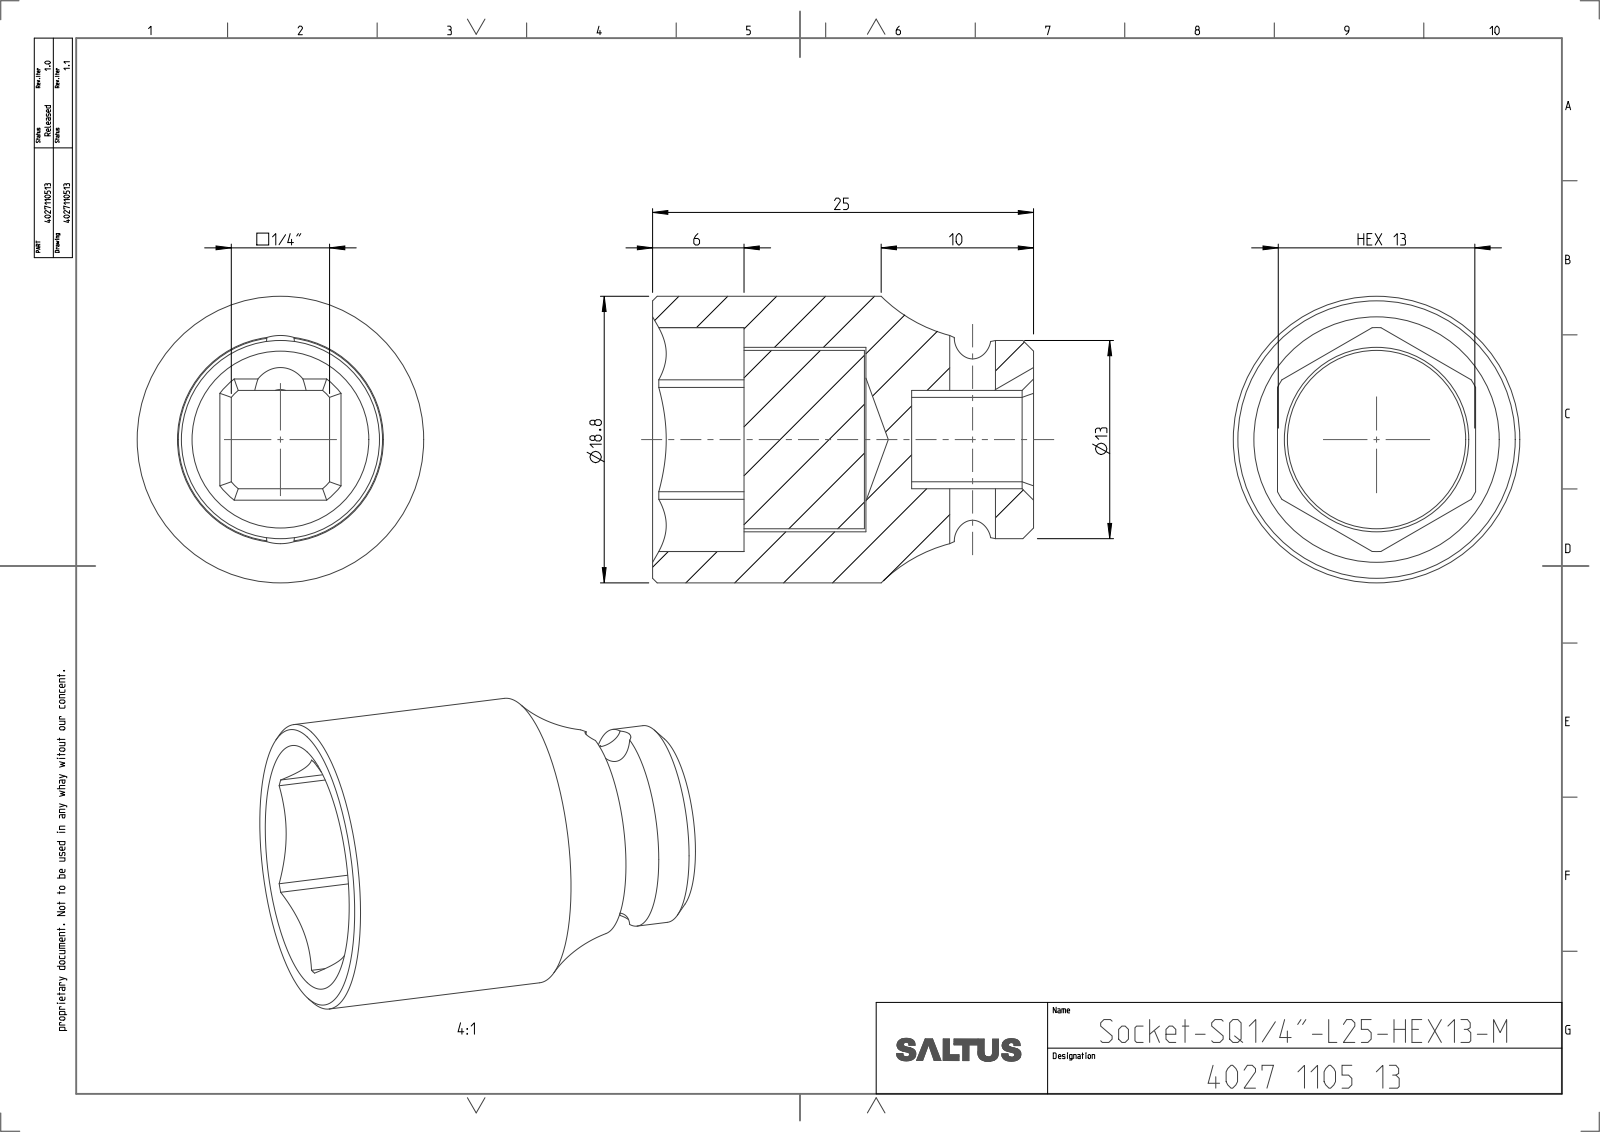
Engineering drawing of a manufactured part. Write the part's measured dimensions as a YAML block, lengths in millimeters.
part_name: "4027110513"
step_written_by: "CREO PARAMETRIC BY PTC INC, 2022414 (CONFIG_CONTROL_DESIGN)"
units: millimeters
bodies: {solids: 2, faces: 63, planar: 24, cylindrical: 23, other: 16}
overall_size: [25, 18.8, 18.8]
volume: 4327
surface_area: 3056
round_holes:
  - {diameter: 3, count: 1}
  - {diameter: 12.1, count: 1}
round_bosses_or_shafts:
  - {diameter: 18.8, count: 1}
  - {diameter: 13, count: 1}
  - {diameter: 11.7, count: 1}
partial_cylinders:
  - {radius: 2, count: 1}
  - {radius: 4.25, count: 1}
  - {radius: 7.34, count: 1}
face_to_face_distances: [13, 7.9, 8, 11, 3.27, 9.73, 6.46, 14, 13.9, 6]
